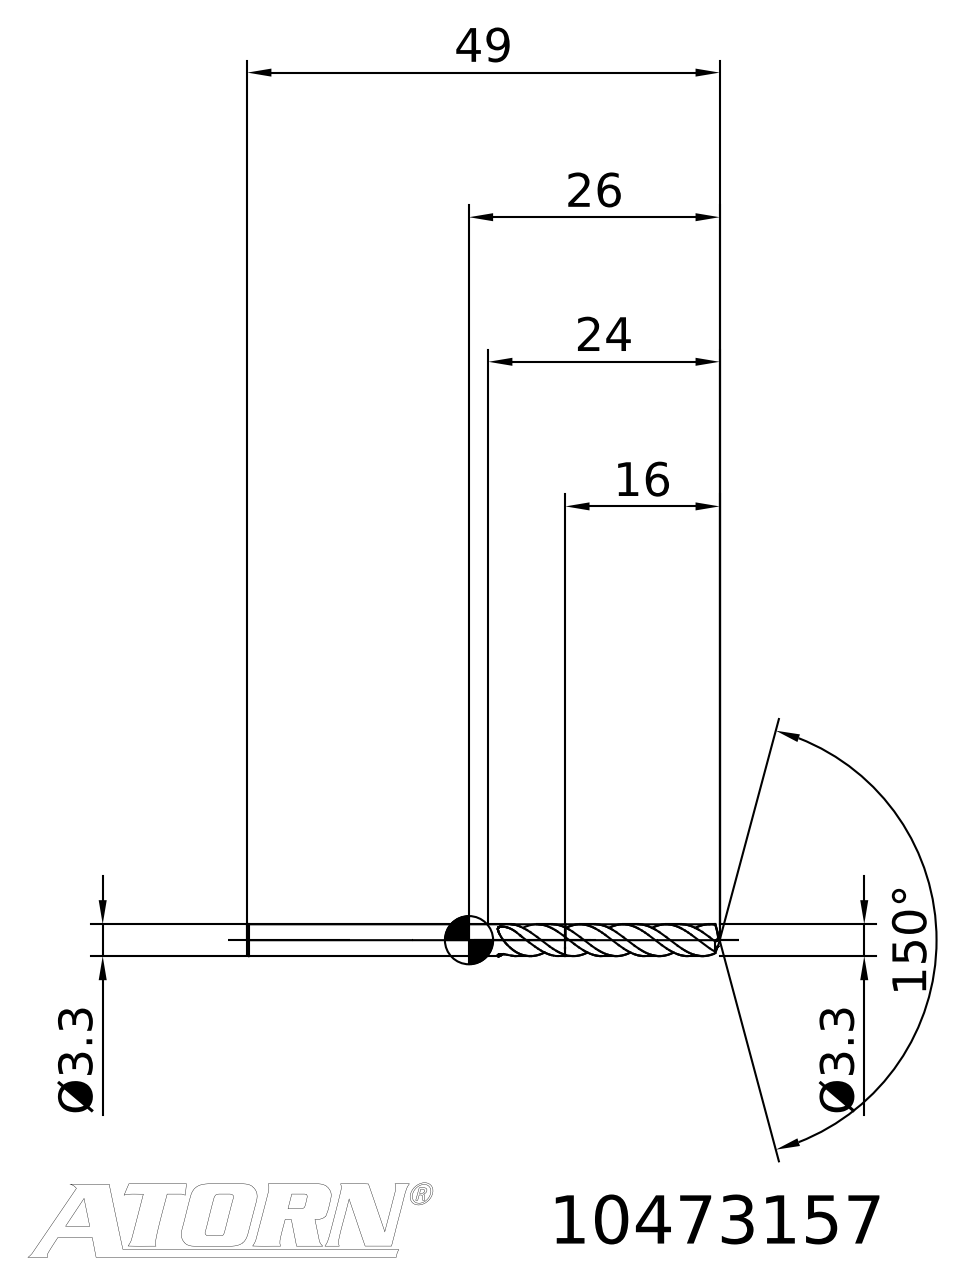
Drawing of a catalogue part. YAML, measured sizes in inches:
step_written_by: "TDM (AUTOMOTIVE_DESIGN)"
units: inches
bodies: {solids: 2, faces: 36, planar: 3, cylindrical: 0, other: 33}
overall_size: [1.929, 0.193, 0.167]
volume: 0.02
surface_area: 0.876
face_to_face_distances: [1.299]
